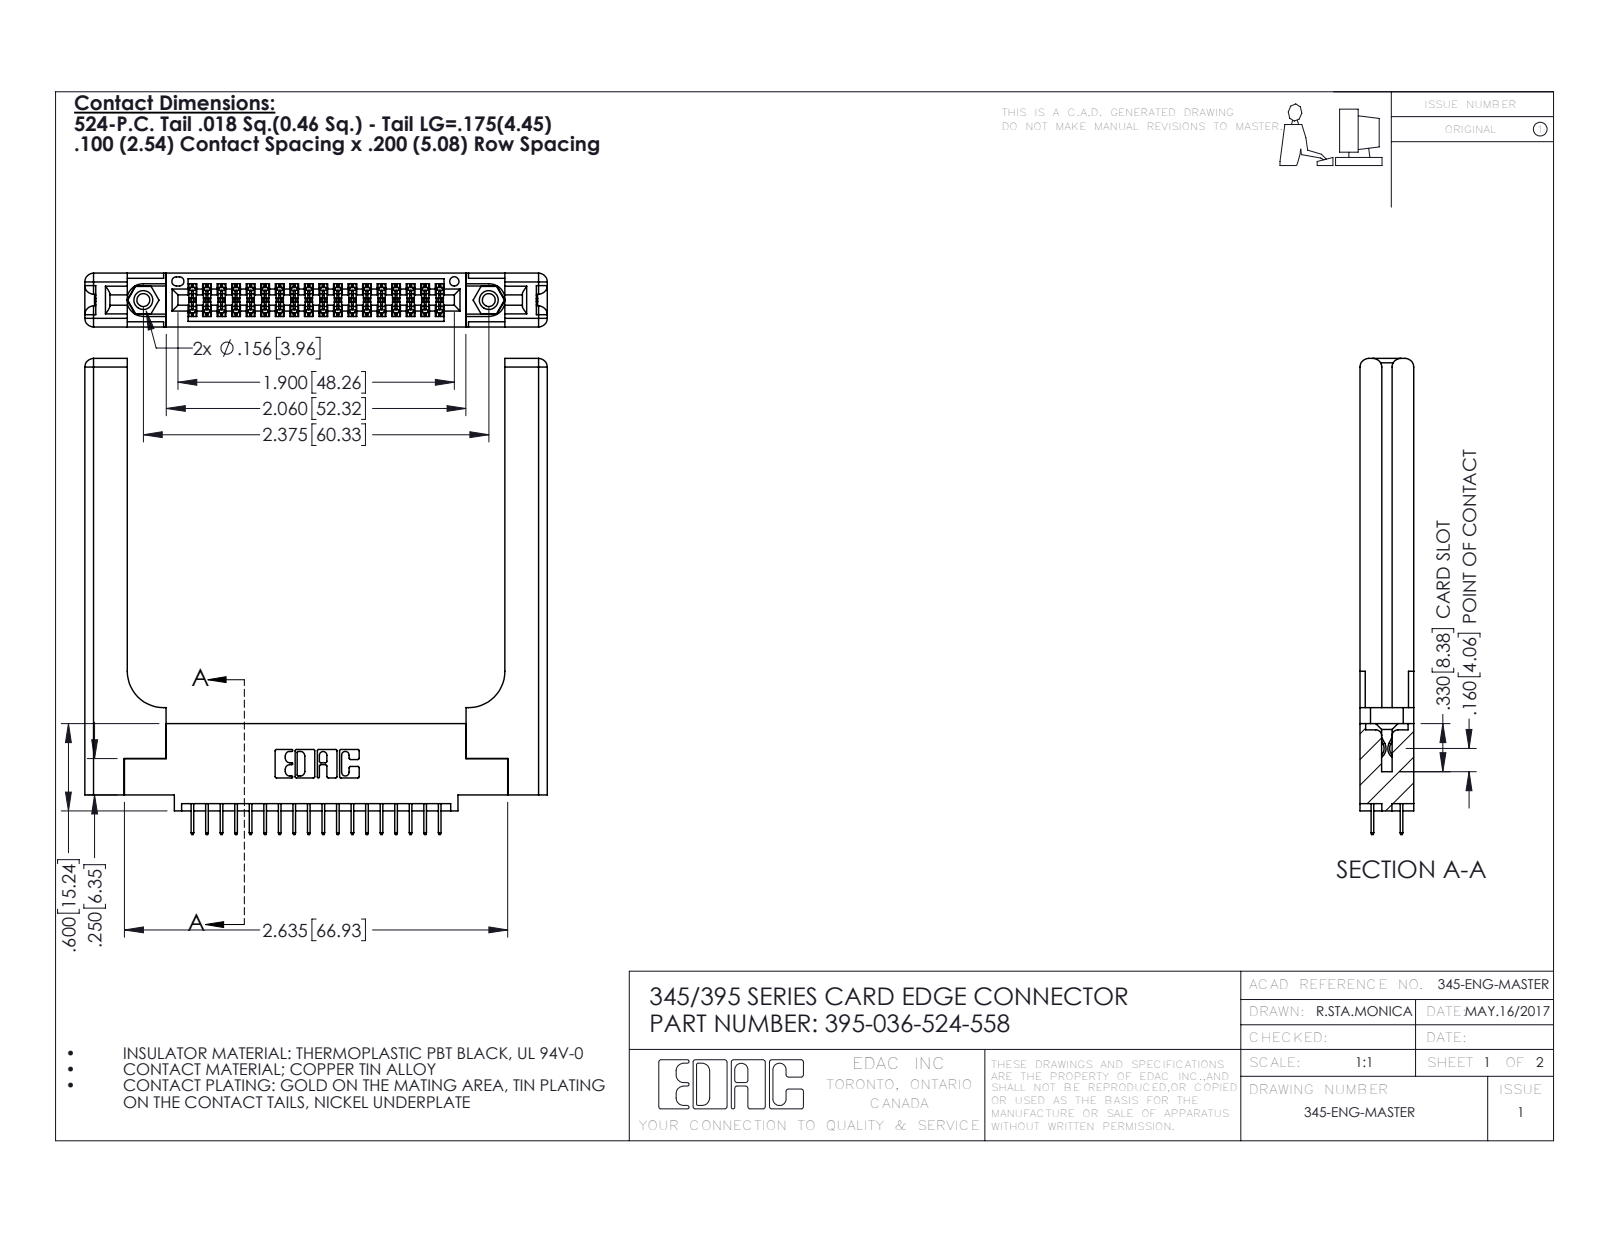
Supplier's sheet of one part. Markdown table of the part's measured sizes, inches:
| quantity | value |
| --- | --- |
| part name | 345-220-058_345-220-058; 345 Part_0.110 Offset - 0.156 Dia-TH; 395-036-524-558; 345-250-001_345-250-001-102 (+1 more) |
| STEP written by | SolidWorks 2016 (CONFIG_CONTROL_DESIGN) |
| units | inches |
| bodies | 41 solids, 2330 faces (1636 planar, 634 cylindrical, 60 other) |
| overall size | 3.272 × 3.179 × 0.37 |
| volume | 0.974 in³ |
| surface area | 24.21 in² |
| round holes (diameter × count) | 0.089 × 2, 0.125 × 2, 0.156 × 2, 0.064 × 1 |
| round bosses / shafts (diameter × count) | 0.155 × 2 |
| partial cylindrical surfaces (radius × count) | 0.006 × 54, 0.01 × 22, 0.06 × 16, 0.007 × 6, 0.031 × 6, 0.026 × 3, 0.014 × 2, 0.019 × 2 |
| main face-to-face distances | 0.37, 0.072, 0.298, 0.148, 0.15, 0.22, 0.077, 0.2, 0.098, 0.272 |
| hole center spacings | 0.27, 2.141, 2.375 |
